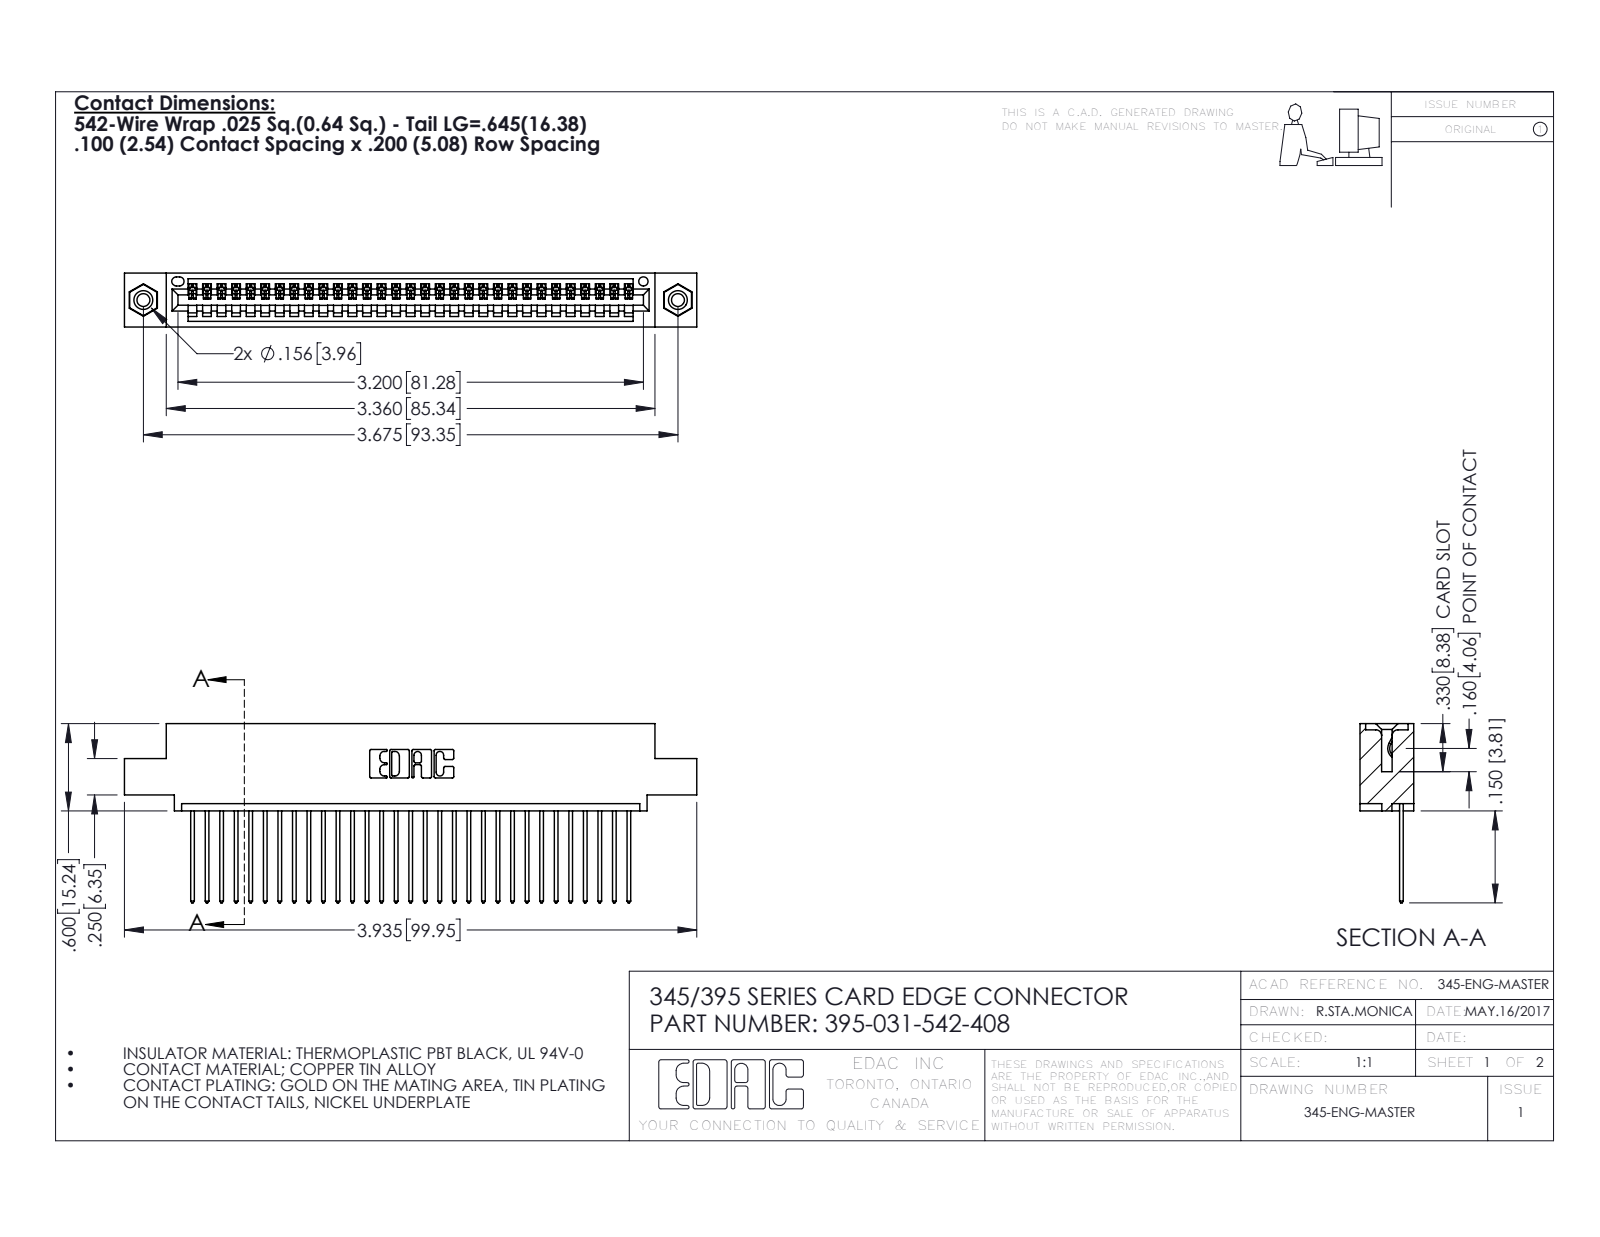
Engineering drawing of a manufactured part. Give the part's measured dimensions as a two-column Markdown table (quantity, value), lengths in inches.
| quantity | value |
| --- | --- |
| part name | 345-292-001_345-293-142; 345 Part_0.110 Offset - 0.156 Dia-TI; 345-250-001_345-250-003-102; 395-031-542-408 |
| STEP written by | SolidWorks 2016 (CONFIG_CONTROL_DESIGN) |
| units | inches |
| bodies | 34 solids, 1988 faces (1356 planar, 616 cylindrical, 16 other) |
| overall size | 3.935 × 1.232 × 0.37 |
| volume | 0.573 in³ |
| surface area | 19.95 in² |
| round holes (diameter × count) | 0.089 × 2, 0.125 × 2, 0.156 × 2, 0.064 × 1 |
| round bosses / shafts (diameter × count) | 0.155 × 2 |
| partial cylindrical surfaces (radius × count) | 0.006 × 62, 0.01 × 62, 0.01 × 22, 0.007 × 6, 0.031 × 6, 0.026 × 3, 0.031 × 2, 0.04 × 2 |
| main face-to-face distances | 0.072, 0.298, 0.37, 0.2, 0.098, 0.272, 0.025, 0.225, 0.149, 0.072 |
| hole center spacings | 0.27, 3.44, 3.675 |
